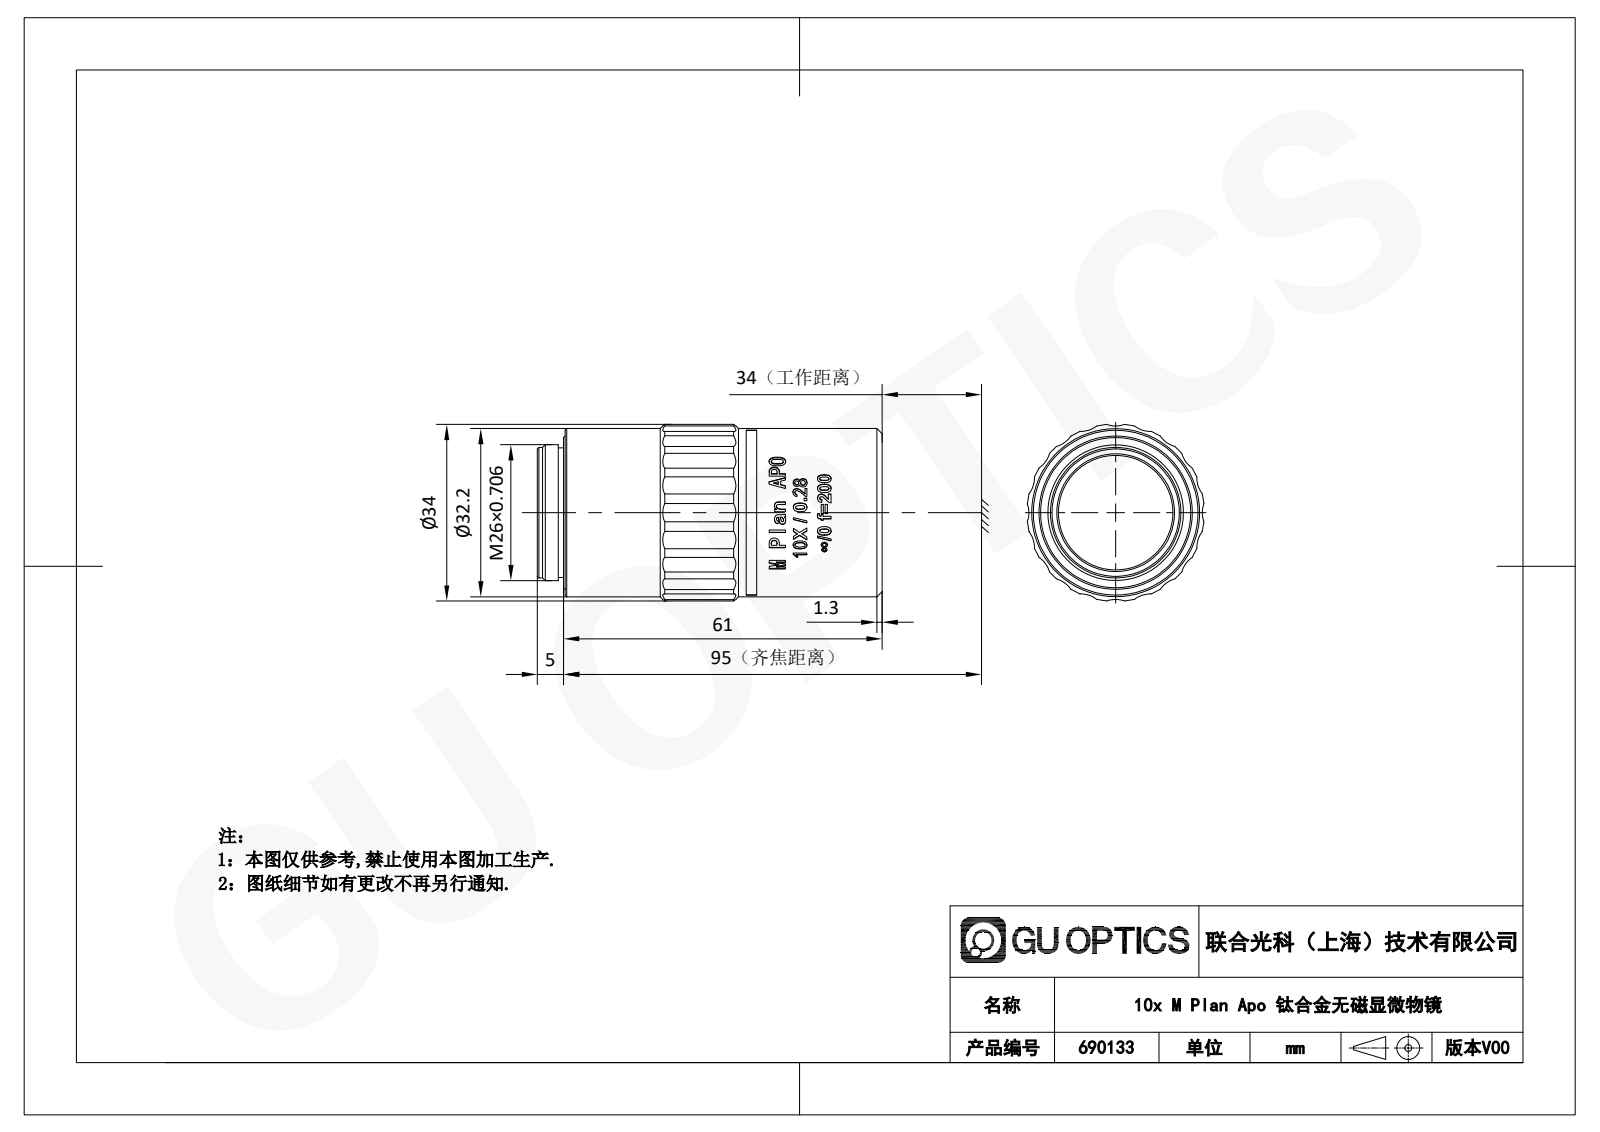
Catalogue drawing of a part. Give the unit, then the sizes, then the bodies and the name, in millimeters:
Units: millimetres
Overall size (bounding box): 66 × 33.82 × 33.82
Round holes (diameter × count): ⌀22 ×1, ⌀24 ×1
Round bosses / shafts (diameter × count): ⌀32.2 ×1, ⌀32 ×1, ⌀26 ×1, ⌀25 ×1, ⌀24.8 ×1
Partial cylindrical surfaces — rounded edges, fillets, slot ends (radius × count): R5 ×20, R15.9 ×1, R17 ×1
Main face-to-face distances: 1.3, 62.3, 61, 1.6, 60.7, 3.7, 5, 5.3, 66, 4
Volume: 51 010 mm³ · Surface area: 8 717 mm²
Bodies: 1 solid, 355 faces (103 planar, 88 cylindrical, 164 other)
Part name (STEP PRODUCT): 690133
STEP written by: SolidWorks 2020 (CONFIG_CONTROL_DESIGN)
